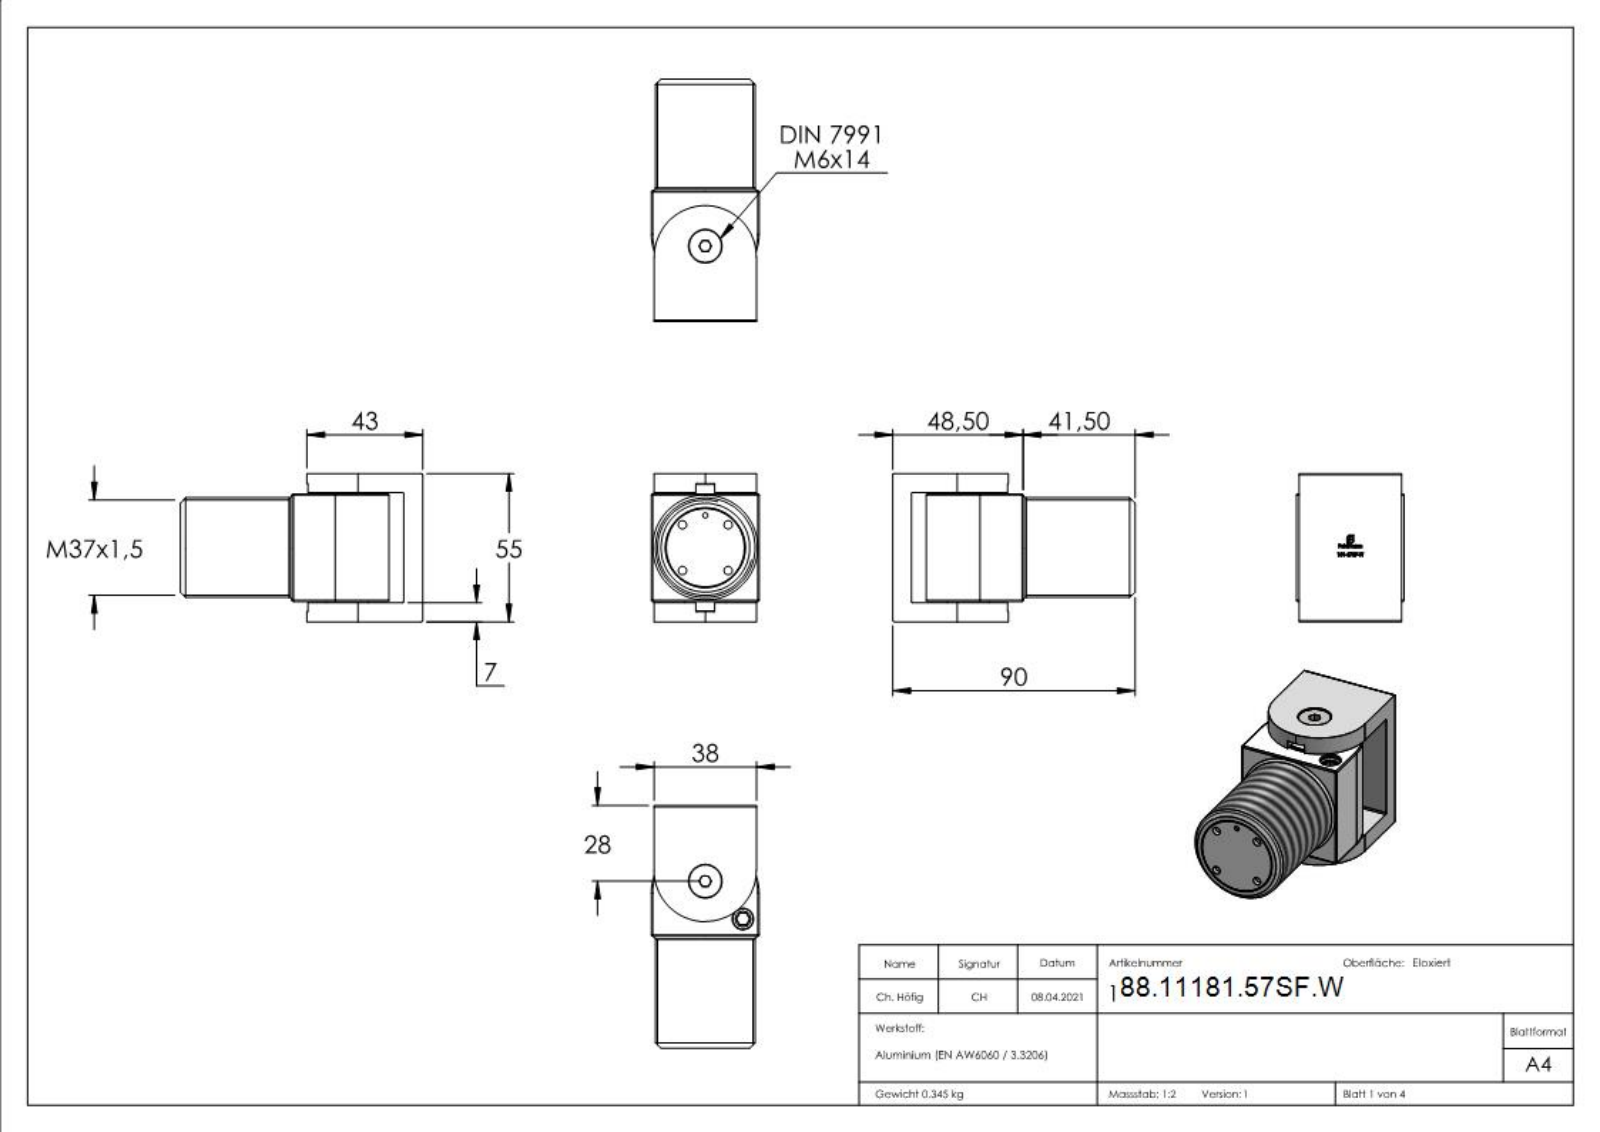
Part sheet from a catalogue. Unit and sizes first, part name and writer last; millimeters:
Units: millimetres
Overall size (bounding box): 14000.45 × 6000 × 6000
Round holes (diameter × count): ⌀3.1 ×4, ⌀1.9 ×1, ⌀5 ×1, ⌀6.5 ×1, ⌀8 ×1, ⌀12.5 ×1, ⌀15.7 ×1, ⌀24 ×1, ⌀29.7 ×1
Round bosses / shafts (diameter × count): ⌀37 ×1, ⌀29.5 ×1, ⌀26 ×1, ⌀23.6 ×1, ⌀15.5 ×1, ⌀12 ×1, ⌀7.8 ×1, ⌀6 ×1
Partial cylindrical surfaces — rounded edges, fillets, slot ends (radius × count): R0.5 ×12, R19 ×1, R20 ×1
Main face-to-face distances: 7, 48, 47.5, 0.5, 7.5, 40.5, 55, 40, 1, 39
Hole centre spacings: 12.01, 16.98, 9.19, 22.18, 24.01, 12, 19.8
Volume: 125 747 mm³ · Surface area: 26 699 mm²
Bodies: 5 solids, 499 faces (247 planar, 80 cylindrical, 172 other)
Part name (STEP PRODUCT): 181-57SF-W; Teil2; DIN-7991 M3-M10; Teil1_181-57SF-W Teil1 (+3 more)
STEP written by: SolidWorks 2018 (CONFIG_CONTROL_DESIGN)
